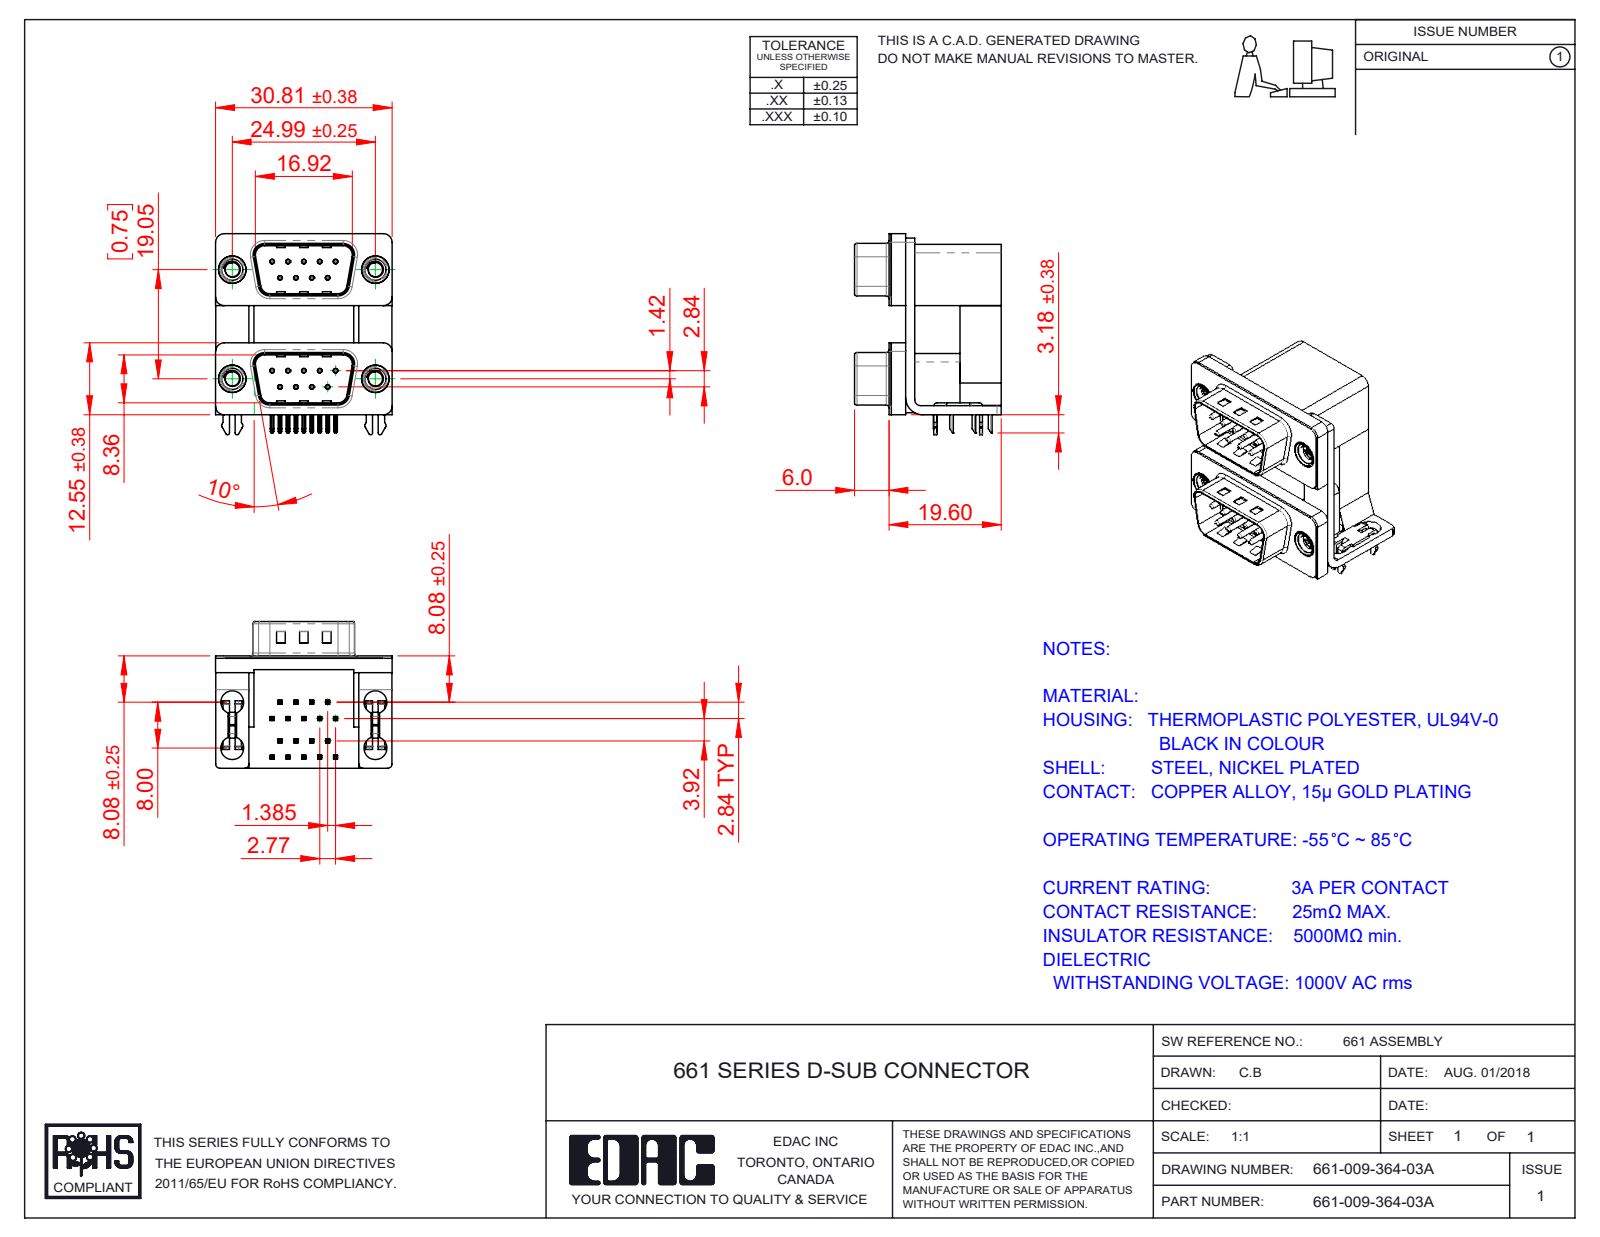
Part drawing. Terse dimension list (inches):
name: 661 2 Prong Board Lock_3; 661 Threaded Rivet_M3; 661 Housing Lower_09 Contacts; 661 Mounting Bracket_2ProngM (+8 more)
written by: SolidWorks 2020 (CONFIG_CONTROL_DESIGN)
unit: in
bodies: 31 solids, 2104 faces (1254 planar, 652 cylindrical, 198 other)
size: 1.382 × 1.213 × 1.008
volume: 0.628 in³; area: 18.72 in²
holes: 18× ⌀0.014, 18× ⌀0.031, 8× ⌀0.157, 4× ⌀0.098, 4× ⌀0.138, 4× ⌀0.189, 4× ⌀0.197
bosses: 18× ⌀0.03, 4× ⌀0.193, 4× ⌀0.187, 4× ⌀0.154
rounds: 82× R0.01, 36× R0.005, 20× R0.02, 14× R0.059, 10× R0.03, 8× R0.035, 8× R0.063, 8× R0.079
face distances: 0.016, 0.098, 0.75, 0.657, 0.756, 0.374, 0.283, 0.421, 0.472, 0.063
hole spacings: 0.124, 0.109, 0.758, 0.75, 0.218, 0.781, 0.641, 0.863
